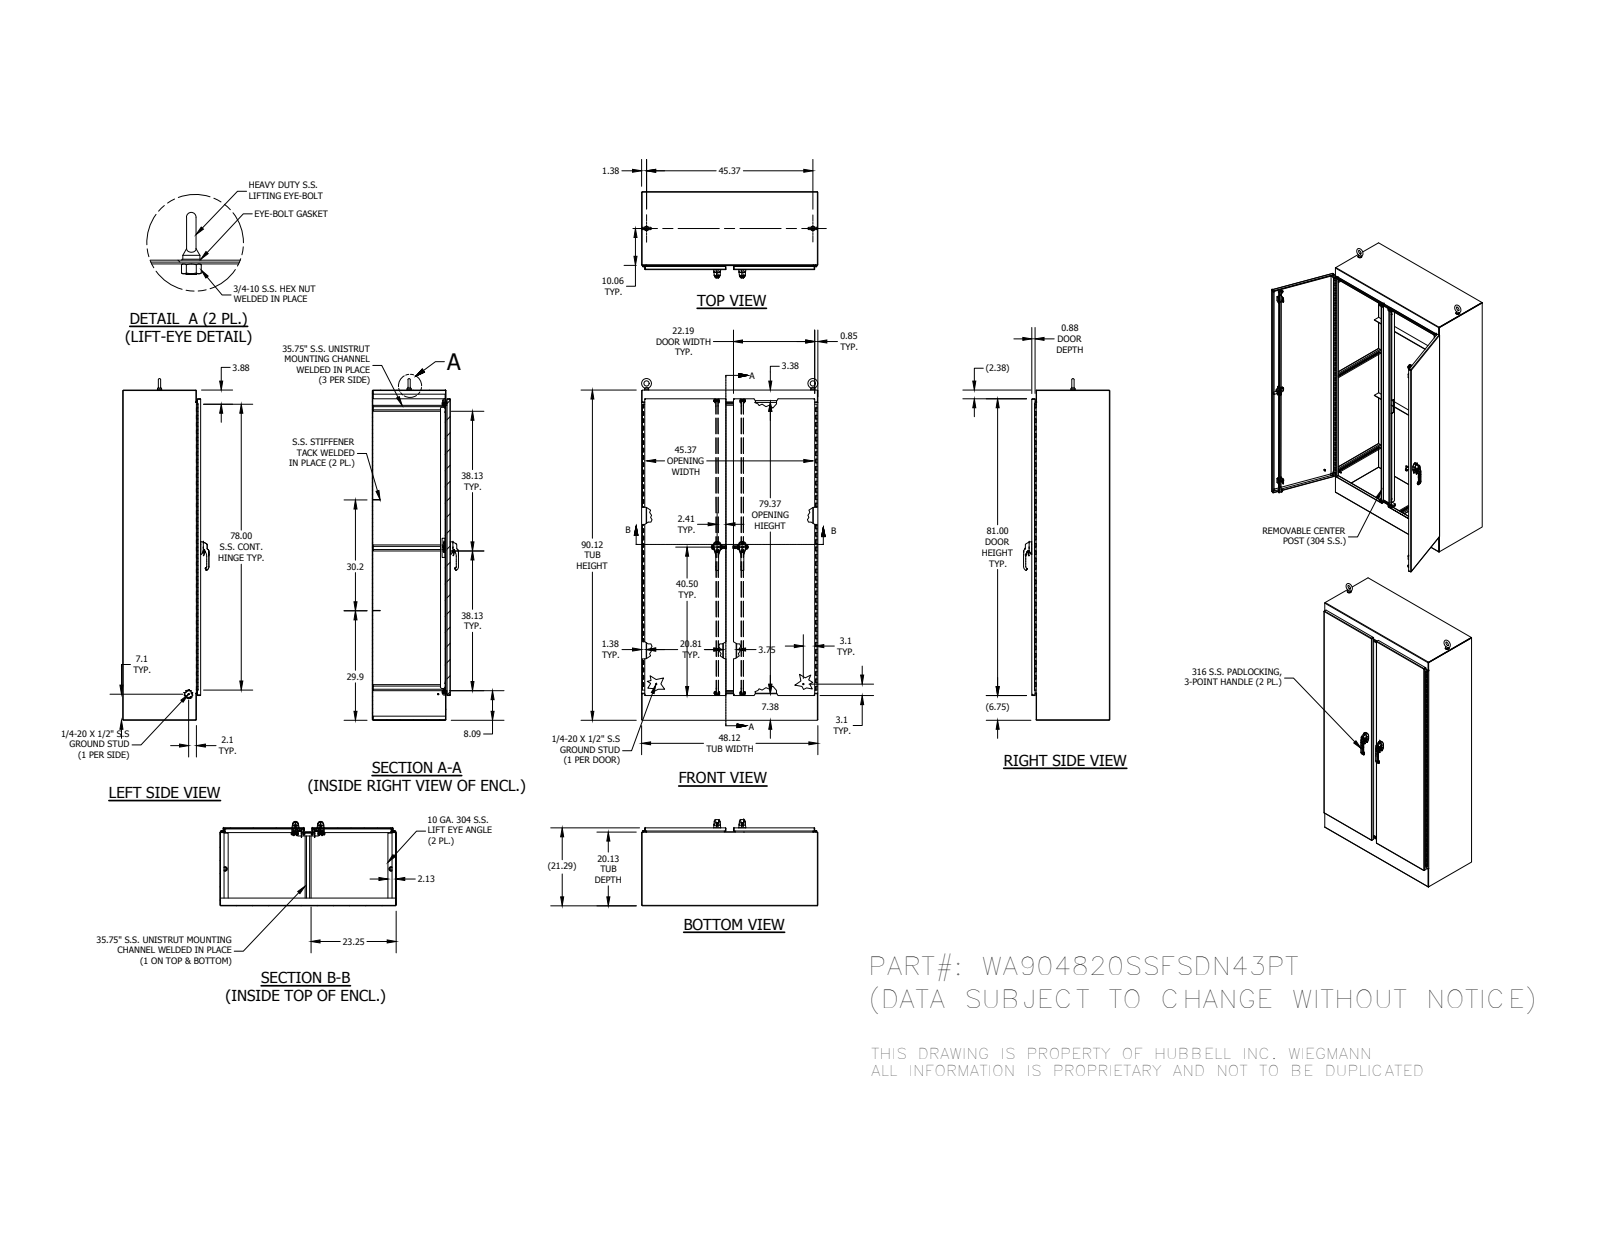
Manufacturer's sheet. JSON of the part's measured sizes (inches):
{"part_name": "LOCK-NUT_AF0; 1091-76; WA9048SSFSDN43PTFB; 2100-11 (+8 more)", "step_written_by": "SolidWorks 2014 (AUTOMOTIVE_DESIGN)", "units": "inches", "bodies": {"solids": 133, "faces": 7276, "planar": 2800, "cylindrical": 2780, "other": 1696}, "overall_size": [93.248, 48.125, 23.541], "volume_in3": 2188, "surface_area_in2": 35854, "round_holes": [[0.262, 16], [0.375, 16], [0.187, 8], [0.213, 6], [0.281, 6], [0.25, 5], [0.196, 4], [0.241, 4], [0.252, 4], [0.281, 4], [0.315, 4], [0.4, 4]], "round_bosses_or_shafts": [[0.25, 7], [0.533, 6], [0.236, 6], [1, 5], [0.563, 4], [0.531, 4], [0.5, 4], [0.438, 4]], "partial_cylinders_radius": [[0.02, 350], [0.012, 214], [0.019, 44], [0.125, 44], [0.05, 34], [0.079, 28], [0.025, 24], [0.059, 24]], "face_to_face_distances": [0.125, 0.125, 21.167, 48, 20, 1.167, 47.875, 90, 21.165, 21.04], "hole_center_spacings": [72.49, 73.24, 26, 0.38, 0.38, 8.667, 0.76, 17.333]}
